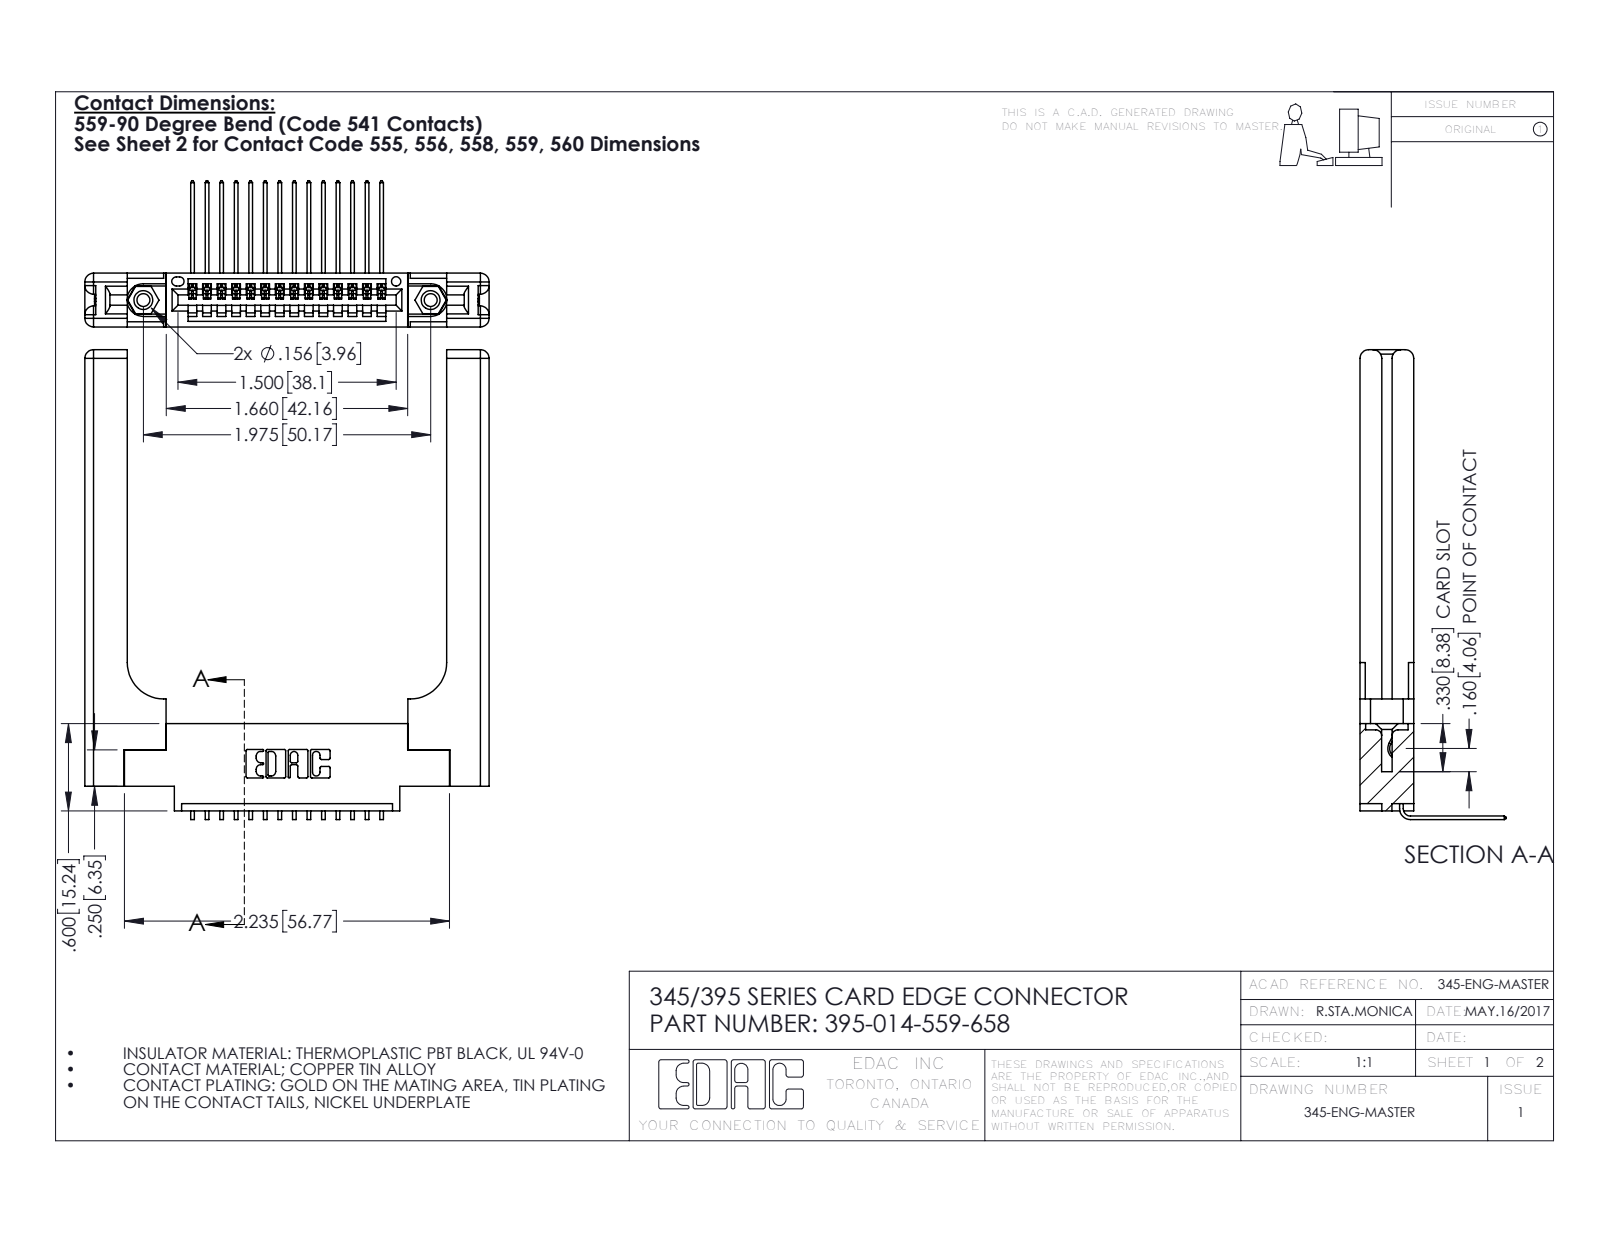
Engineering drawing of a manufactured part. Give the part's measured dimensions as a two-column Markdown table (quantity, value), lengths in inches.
| quantity | value |
| --- | --- |
| part name | 345-292-001_558 559 Tail - 1; 345 Part_0.170 Offset - 0.156 Dia-TH; 395-014-559-658; 345-220-058_345-220-058 (+1 more) |
| STEP written by | SolidWorks 2016 (CONFIG_CONTROL_DESIGN) |
| units | inches |
| bodies | 19 solids, 1226 faces (820 planar, 346 cylindrical, 60 other) |
| overall size | 3.229 × 2.779 × 1.005 |
| volume | 0.91 in³ |
| surface area | 21.45 in² |
| round holes (diameter × count) | 0.089 × 2, 0.125 × 2, 0.156 × 2, 0.064 × 1 |
| round bosses / shafts (diameter × count) | 0.155 × 2 |
| partial cylindrical surfaces (radius × count) | 0.006 × 28, 0.01 × 22, 0.06 × 16, 0.007 × 6, 0.031 × 6, 0.026 × 3, 0.03 × 2, 0.031 × 2 |
| main face-to-face distances | 0.37, 0.072, 0.15, 0.298, 0.148, 0.077, 0.22, 0.12, 2.196, 0.225 |
| hole center spacings | 0.27, 1.742, 1.975 |
